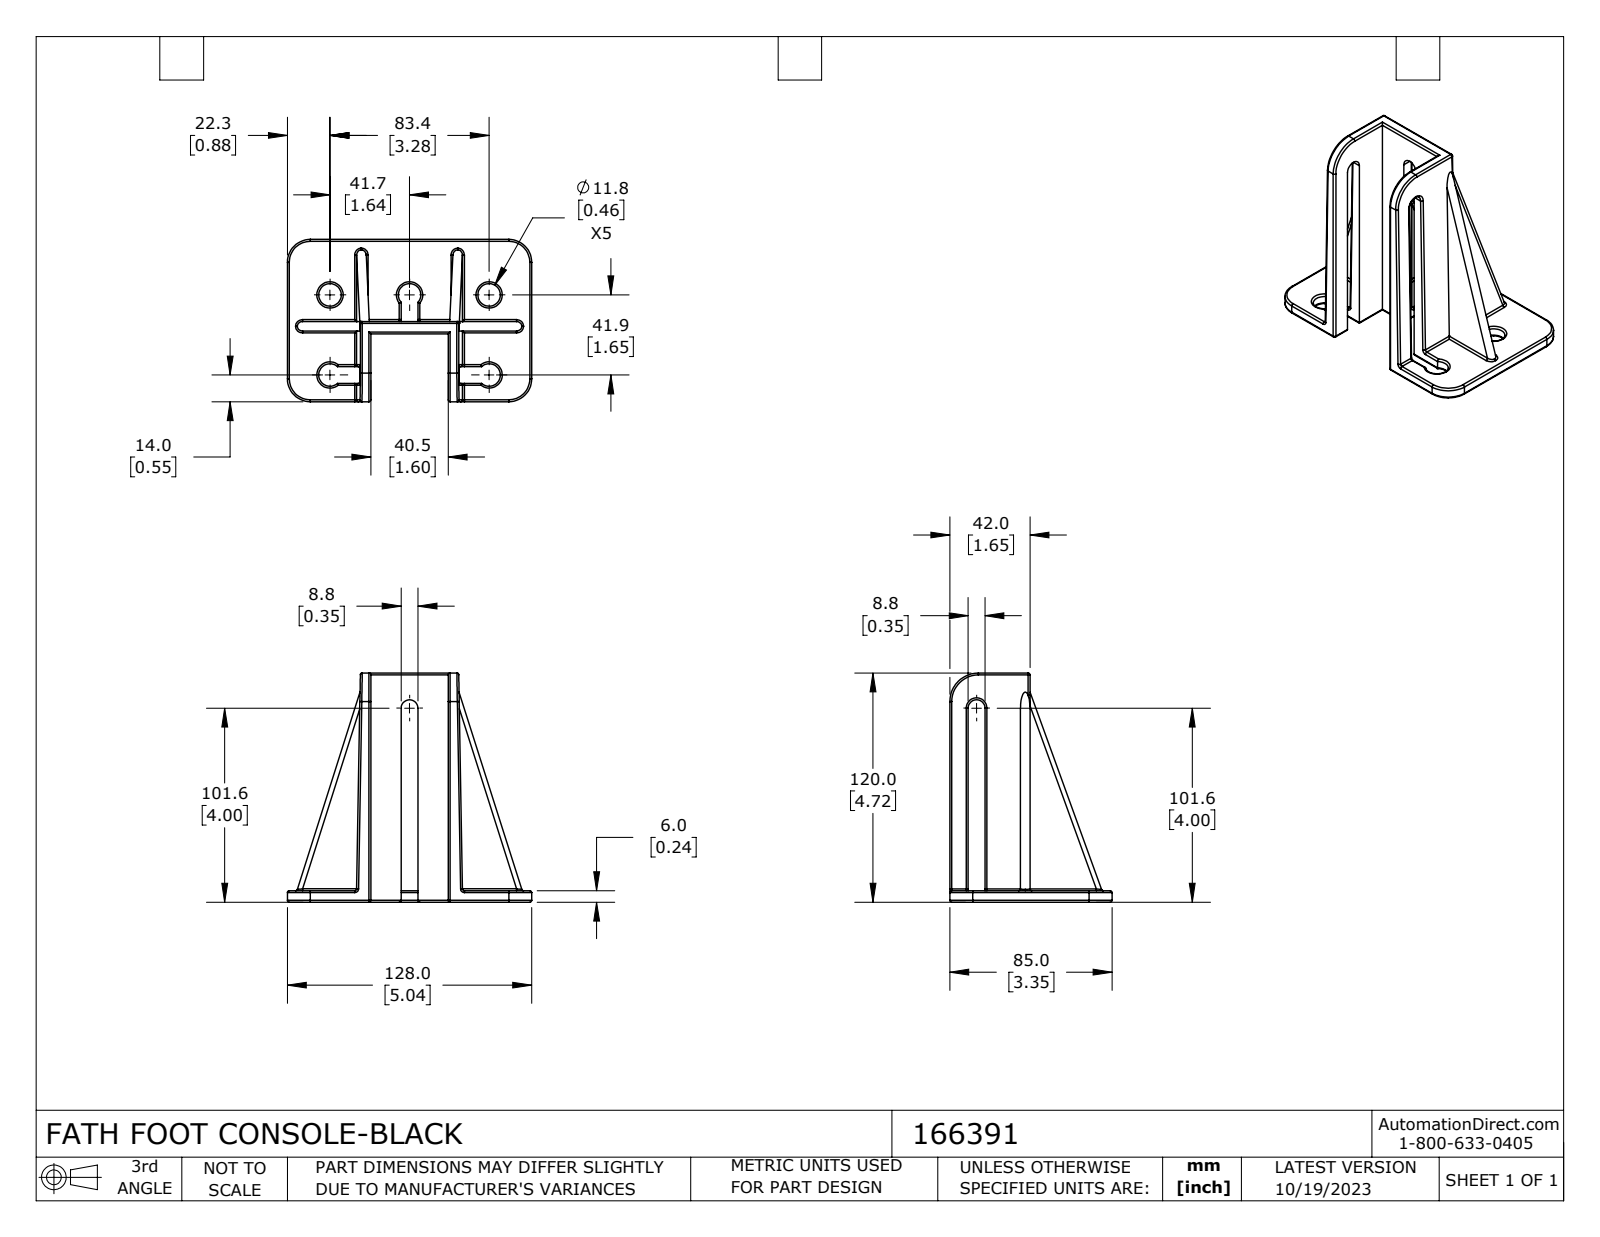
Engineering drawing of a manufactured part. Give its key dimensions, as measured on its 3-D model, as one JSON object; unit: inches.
{"part_name": "166391", "step_written_by": "SolidWorks 2023 (CONFIG_CONTROL_DESIGN)", "units": "inches", "bodies": {"solids": 1, "faces": 172, "planar": 28, "cylindrical": 85, "other": 59}, "overall_size": [5.039, 4.724, 3.346], "volume_in3": 9.693, "surface_area_in2": 94.54, "round_holes": [[0.465, 2]], "partial_cylinders_radius": [[0.039, 43], [0.098, 4], [0.472, 4], [0.232, 3], [0.173, 2], [0.591, 1]], "face_to_face_distances": [0.236, 0.197, 0.256, 1.595, 0.059, 0.346, 1.02, 1.079, 1.276, 0.673], "hole_center_spacings": [3.282]}
